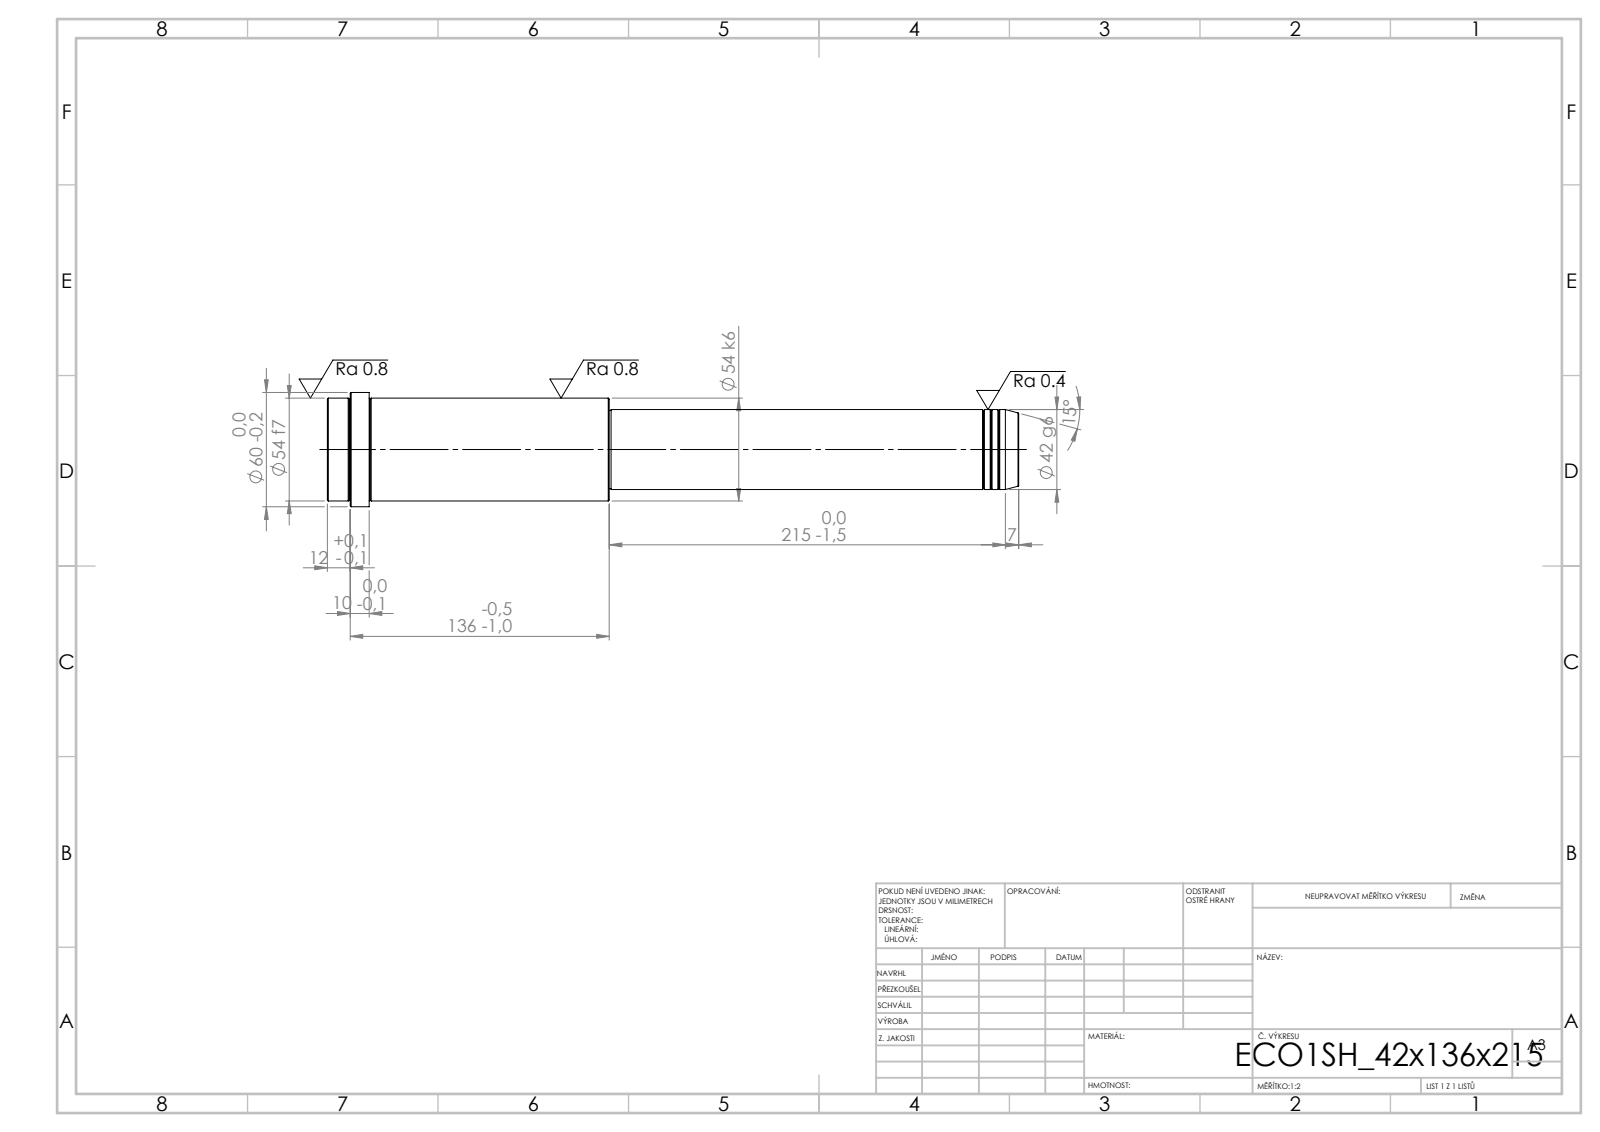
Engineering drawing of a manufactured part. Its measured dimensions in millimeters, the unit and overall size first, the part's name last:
Units: millimetres
Overall size (bounding box): 363 × 60 × 60
Round bosses / shafts (diameter × count): ⌀60 ×1, ⌀54 ×1, ⌀42 ×1, ⌀41 ×1
Main face-to-face distances: 363, 215, 148, 341, 126, 22, 351, 136, 10, 12
Volume: 640 934 mm³ · Surface area: 59 435 mm²
Bodies: 1 solid, 52 faces (6 planar, 16 cylindrical, 30 other)
STEP written by: SolidWorks 2019 (CONFIG_CONTROL_DESIGN)
